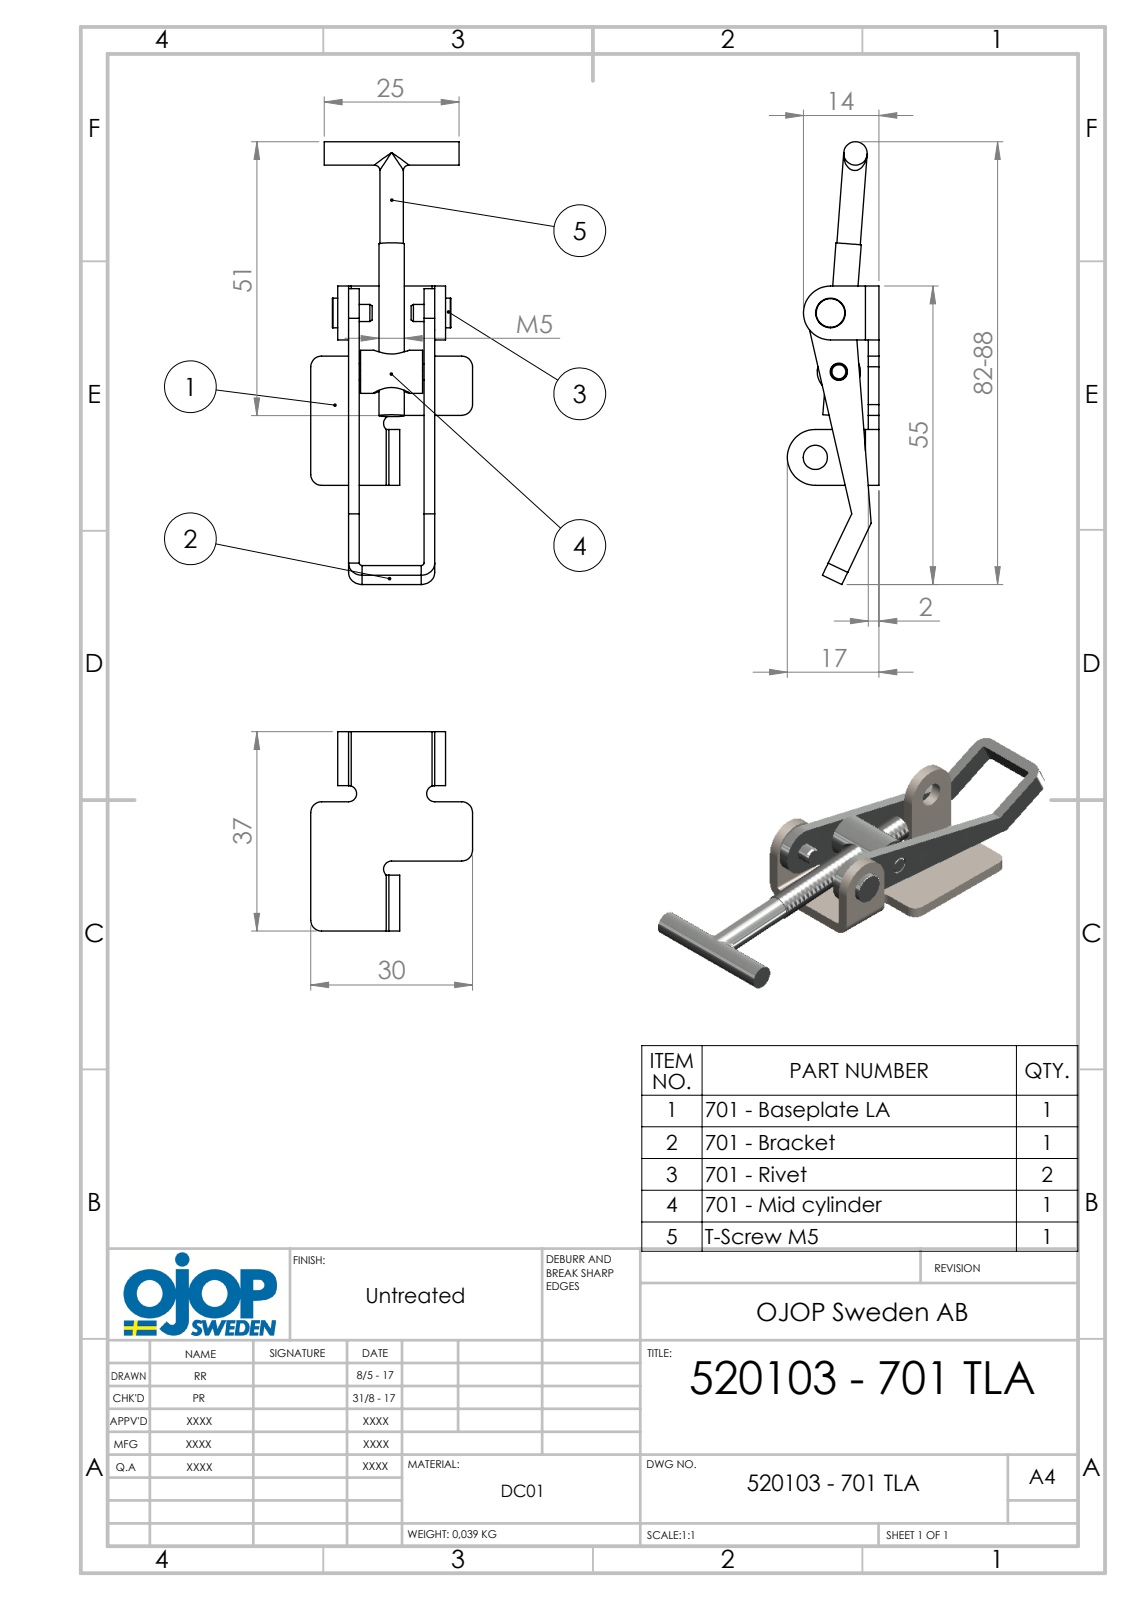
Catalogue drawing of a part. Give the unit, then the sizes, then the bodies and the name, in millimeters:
Units: millimetres
Overall size (bounding box): 79.88 × 30 × 17
Round holes (diameter × count): ⌀3.2 ×2, ⌀4.5 ×2, ⌀4.8 ×1
Round bosses / shafts (diameter × count): ⌀4.36 ×2, ⌀8 ×1, ⌀5.5 ×1, ⌀4.7 ×1, ⌀3.15 ×1, ⌀3 ×1
Partial cylindrical surfaces — rounded edges, fillets, slot ends (radius × count): R0.5 ×5, R2.5 ×5, R2 ×4, R1.5 ×3, R4.5 ×1, R5 ×1, R5.19 ×1
Main face-to-face distances: 2, 14, 16, 12, 4, 6.5, 7.5, 9.5, 8.5, 18
Hole centre spacings: 11.02, 16.49, 26.96
Volume: 5 210 mm³ · Surface area: 6 320 mm²
Bodies: 6 solids, 147 faces (63 planar, 66 cylindrical, 18 other)
Part name (STEP PRODUCT): 720951 - T-skruv 701 FZB; 520103 - 701 TLA; 701 - Bygel; 701 - LA (+2 more)
STEP written by: SolidWorks 2015 (AUTOMOTIVE_DESIGN)
